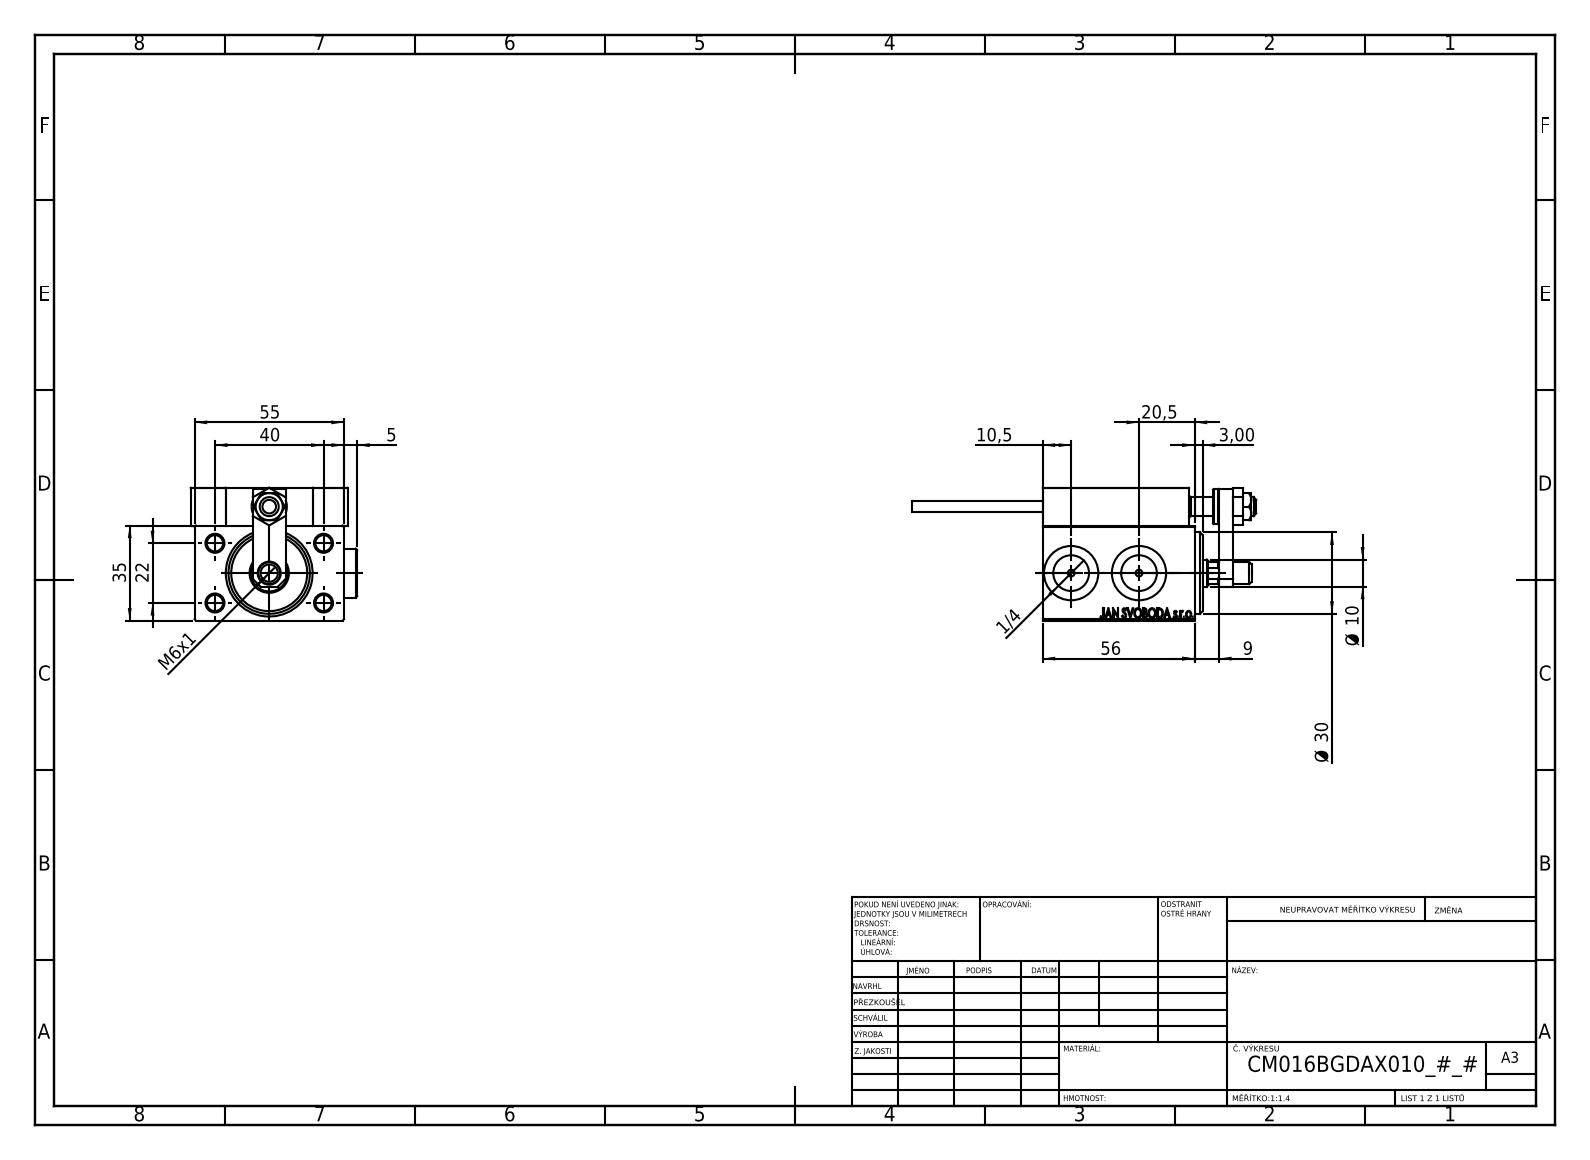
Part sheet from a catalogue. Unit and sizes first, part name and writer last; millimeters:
Units: millimetres
Overall size (bounding box): 126.7 × 61.4 × 49
Round holes (diameter × count): ⌀8 ×5, ⌀3.2 ×4, ⌀4 ×4, ⌀6 ×4, ⌀2.5 ×2, ⌀5 ×2, ⌀13.16 ×2, ⌀20 ×2, ⌀4.5 ×1, ⌀7 ×1, ⌀8.5 ×1, ⌀10 ×1
Round bosses / shafts (diameter × count): ⌀18 ×2, ⌀5 ×2, ⌀3.8 ×2, ⌀13 ×1, ⌀11 ×1, ⌀8 ×1, ⌀6 ×1
Partial cylindrical surfaces — rounded edges, fillets, slot ends (radius × count): R0.3 ×26, R3 ×2, R4.5 ×1
Main face-to-face distances: 35, 14, 49, 5, 3, 10, 1.5, 7, 55, 13
Hole centre spacings: 22.83, 8.25, 11.37, 20, 22, 23.41, 24.13, 29.59
Volume: 143 342 mm³ · Surface area: 49 896 mm²
Bodies: 27 solids, 1386 faces (599 planar, 204 cylindrical, 583 other)
Part name (STEP PRODUCT): SWITCH X; Block; ALLEN BOLT D5; ZARAZKA (+8 more)
STEP written by: SolidWorks 2019 (CONFIG_CONTROL_DESIGN)
